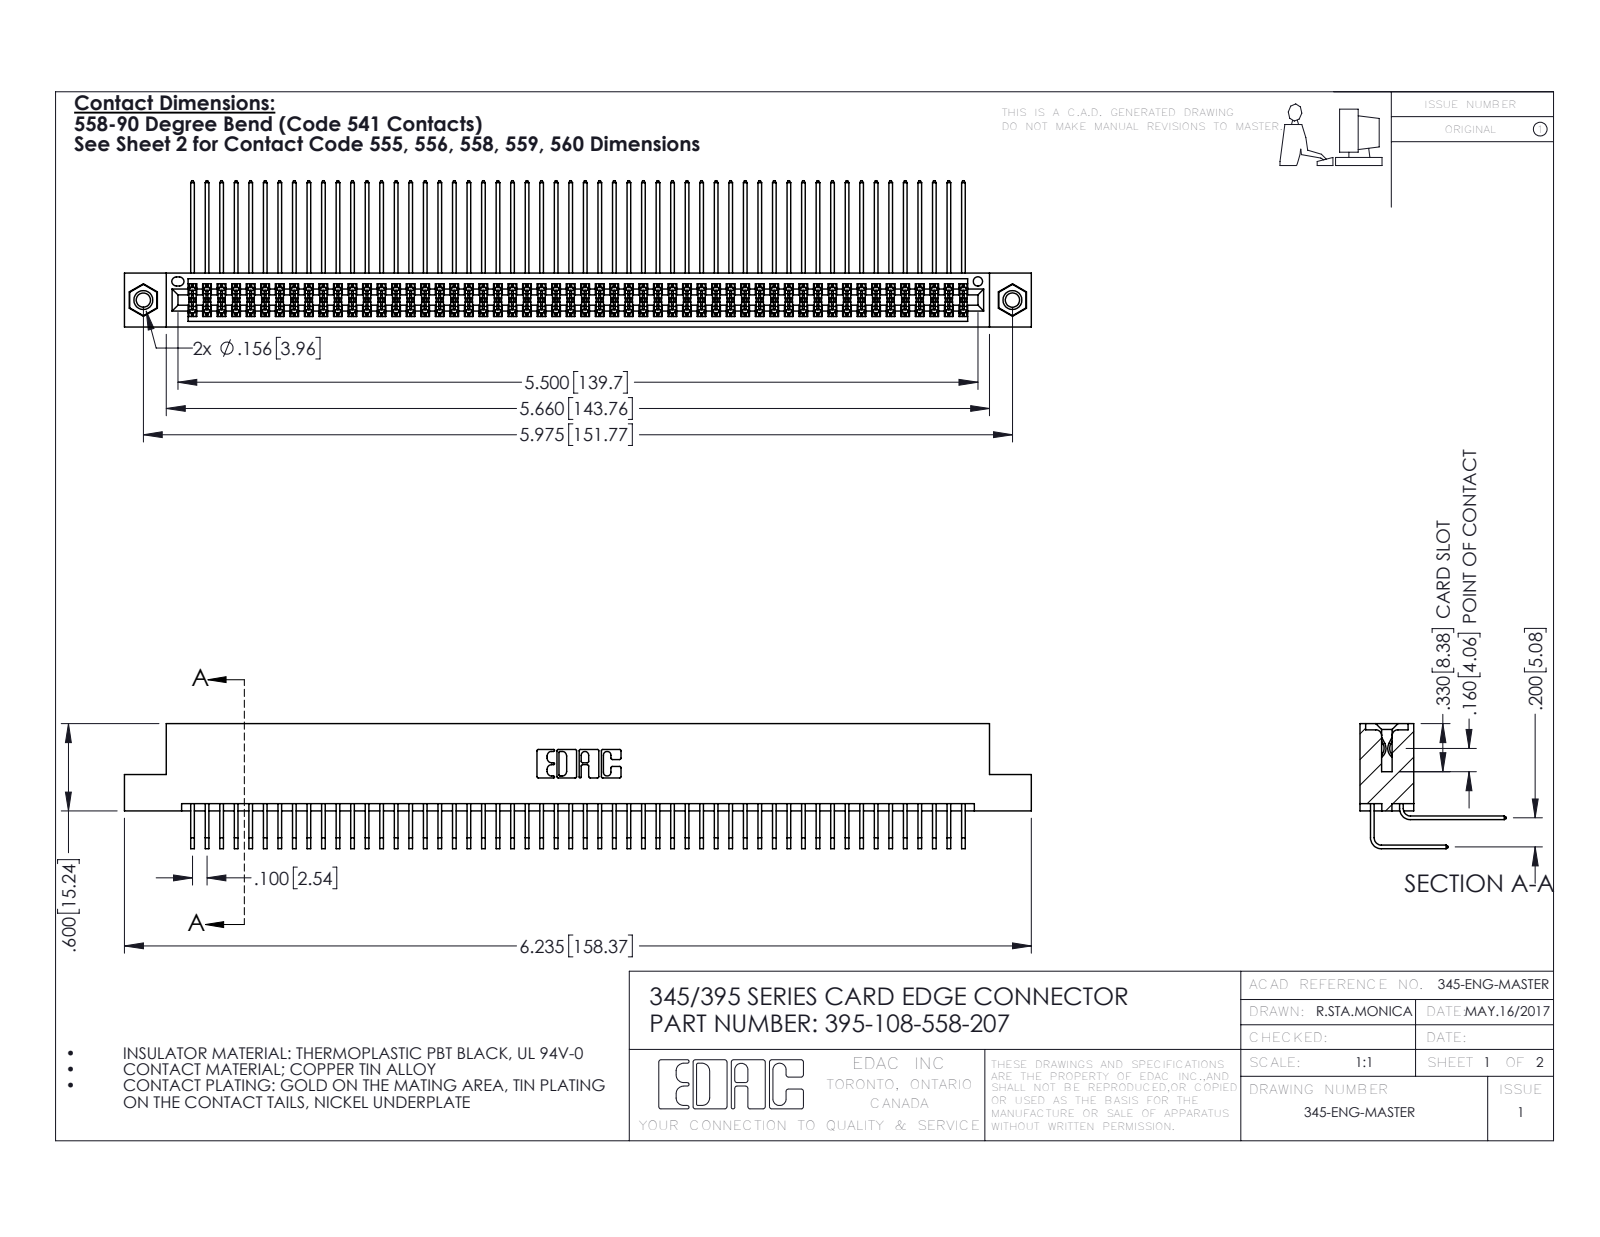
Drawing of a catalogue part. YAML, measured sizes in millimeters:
part_name: "345-292-001_558 559 Tail - 1; 395-108-558-207; 345-250-001_345-250-005-103; 345-292-001_558 Tail - 2 (+1 more)"
step_written_by: "SolidWorks 2016 (CONFIG_CONTROL_DESIGN)"
units: millimeters
bodies: {solids: 111, faces: 5802, planar: 3892, cylindrical: 1894, other: 16}
overall_size: [158.4, 25.5, 21.8]
volume: 16100
surface_area: 26990
round_holes:
  - {diameter: 2.5, count: 2}
  - {diameter: 3.2, count: 2}
  - {diameter: 4, count: 2}
  - {diameter: 1.6, count: 1}
round_bosses_or_shafts:
  - {diameter: 3.9, count: 2}
partial_cylinders:
  - {radius: 0.2, count: 162}
  - {radius: 0.3, count: 22}
  - {radius: 0.2, count: 6}
  - {radius: 0.8, count: 6}
  - {radius: 0.7, count: 3}
  - {radius: 0.4, count: 2}
  - {radius: 0.5, count: 2}
  - {radius: 0.6, count: 2}
face_to_face_distances: [1.8, 7.6, 5.1, 9.4, 2.5, 6.9, 0.6, 5.7, 0.6, 4.4]
hole_center_spacings: [6.9, 145.8, 151.8]
